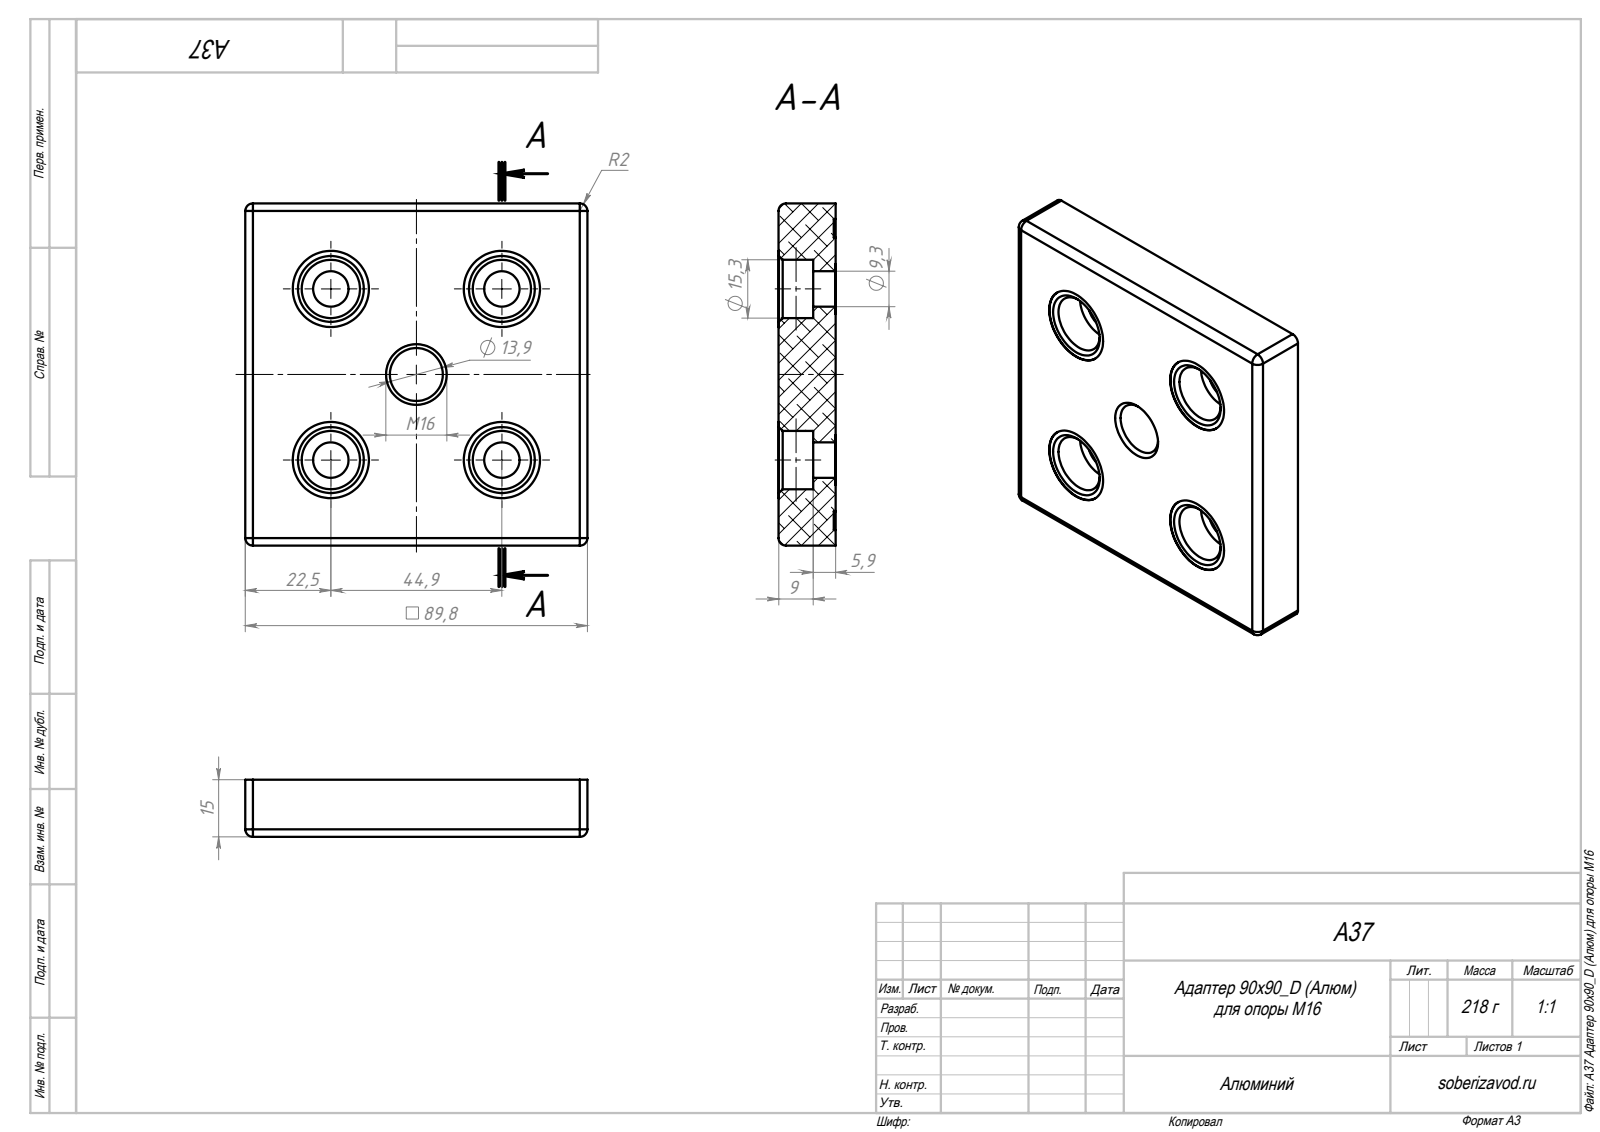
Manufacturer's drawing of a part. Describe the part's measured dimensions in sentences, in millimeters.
Its 3-D file was written by "SolidWorks 2018 (AUTOMOTIVE_DESIGN)". It is 1 solid with 165 faces: 66 planar, 83 cylindrical and 16 other. Overall it measures 89.8 by 89.8 by 15 millimeters. Its volume is 83 229 cubic millimeters and its surface area 29 954 square millimeters. Round holes: 12 of diameter 4.9, 4 of diameter 9.3, 4 of diameter 13, 4 of diameter 15.3, 4 of diameter 20, 1 of diameter 13.9. Partial cylindrical surfaces (rounded edges, fillets, slot ends): 8 of radius 2, 4 of radius 13.95, 1 of radius 24.95. The main face-to-face distances are 15, 3.9, 85.9, 10.9, 4.1, 89.8, 82, 5.9, 5, 9.1. The hole center spacings are 15.9, 27.76, 36.3, 43.46, 44.44, 44.9, 47.63, 51.77.
